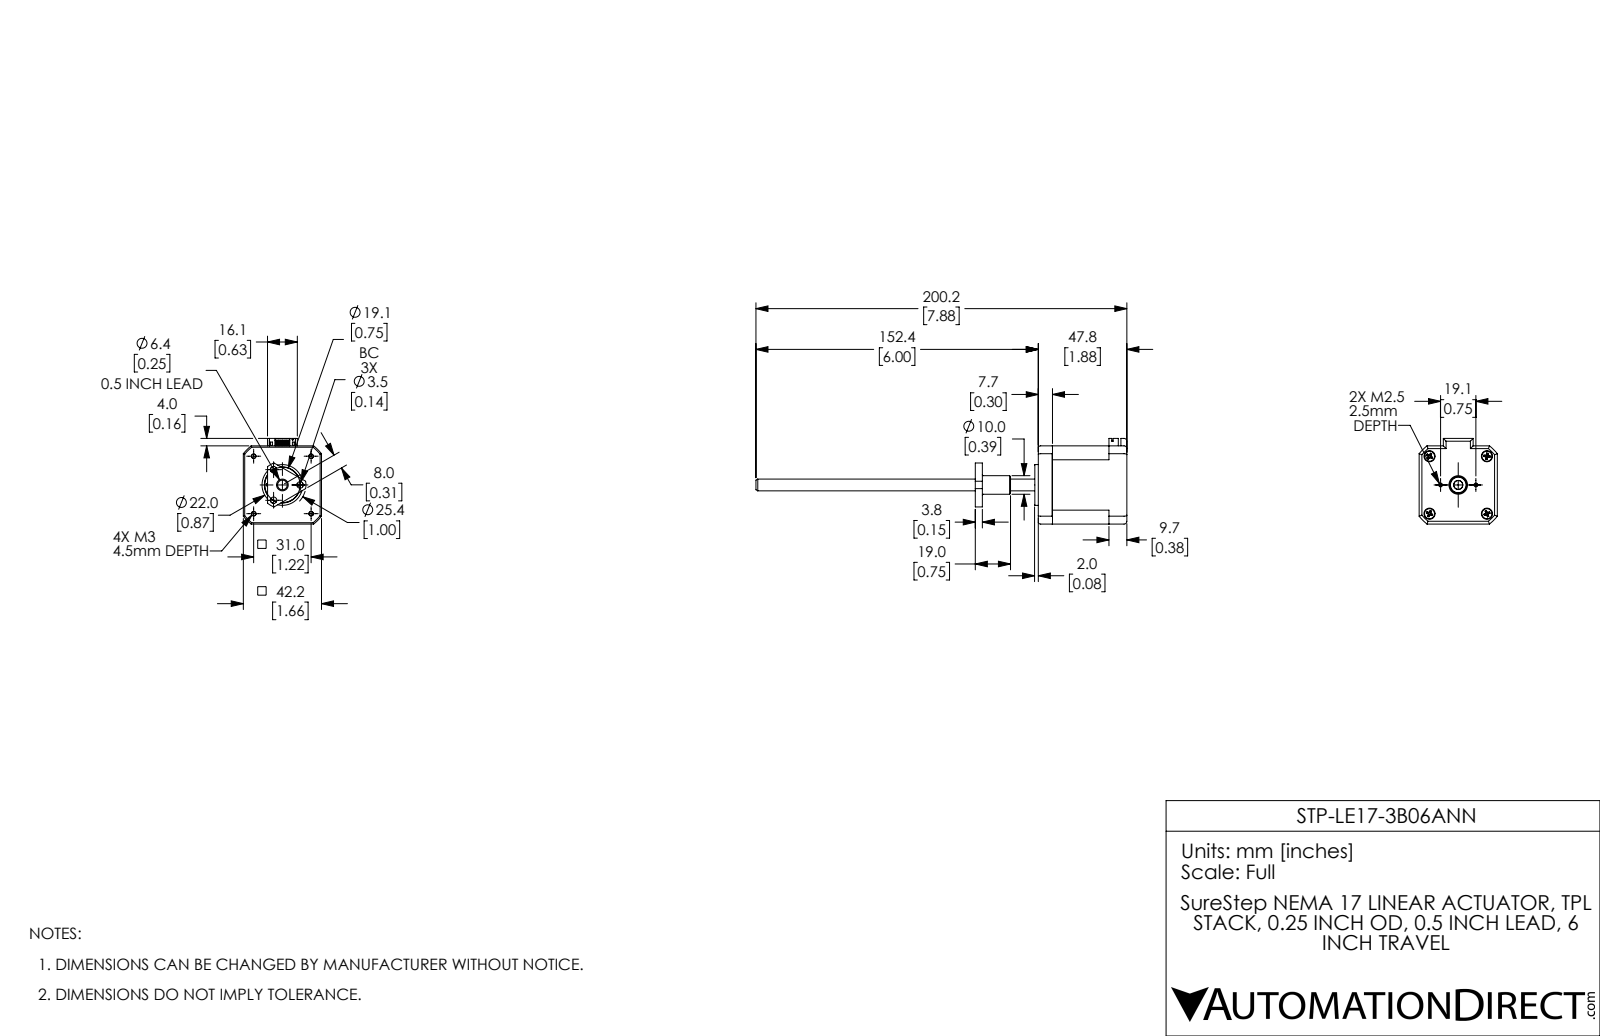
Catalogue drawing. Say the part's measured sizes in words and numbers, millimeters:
The part is named "STP-LE17-3B06ANN; STP-LE17-3B06ANN_2; STP-LE17-3B06ANN_1". Its 3-D file was written by "SolidWorks 2017 (AUTOMOTIVE_DESIGN)". It is 5 solids with 729 faces: 364 planar, 236 cylindrical and 129 other. Overall it measures 200.2 by 46.2 by 42.2 millimeters. Its volume is 78 097 cubic millimeters and its surface area 28 352 square millimeters. Round holes: 4 of diameter 2.5, 4 of diameter 3.8, 4 of diameter 6, 3 of diameter 3.5, 2 of diameter 1.5, 2 of diameter 2.05, 1 of diameter 4.9, 1 of diameter 13, 1 of diameter 17, 1 of diameter 19.46, 1 of diameter 20. Round bosses or shafts: 4 of diameter 5.4, 4 of diameter 2.91, 1 of diameter 27, 1 of diameter 25.91, 1 of diameter 22, 1 of diameter 12, 1 of diameter 10, 1 of diameter 9. Partial cylindrical surfaces (rounded edges, fillets, slot ends): 12 of radius 1, 11 of radius 1.5, 2 of radius 2.5, 1 of radius 0.7, 1 of radius 12.7, 1 of radius 14.25, 1 of radius 16, 1 of radius 25.1. The main face-to-face distances are 42.2, 9.65, 47.8, 40.15, 38.15, 1.6, 30.5, 7.65, 45.3, 40.6. The hole center spacings are 16.61, 9.52, 21.92, 29.43, 31, 4.93, 8, 12.96.
